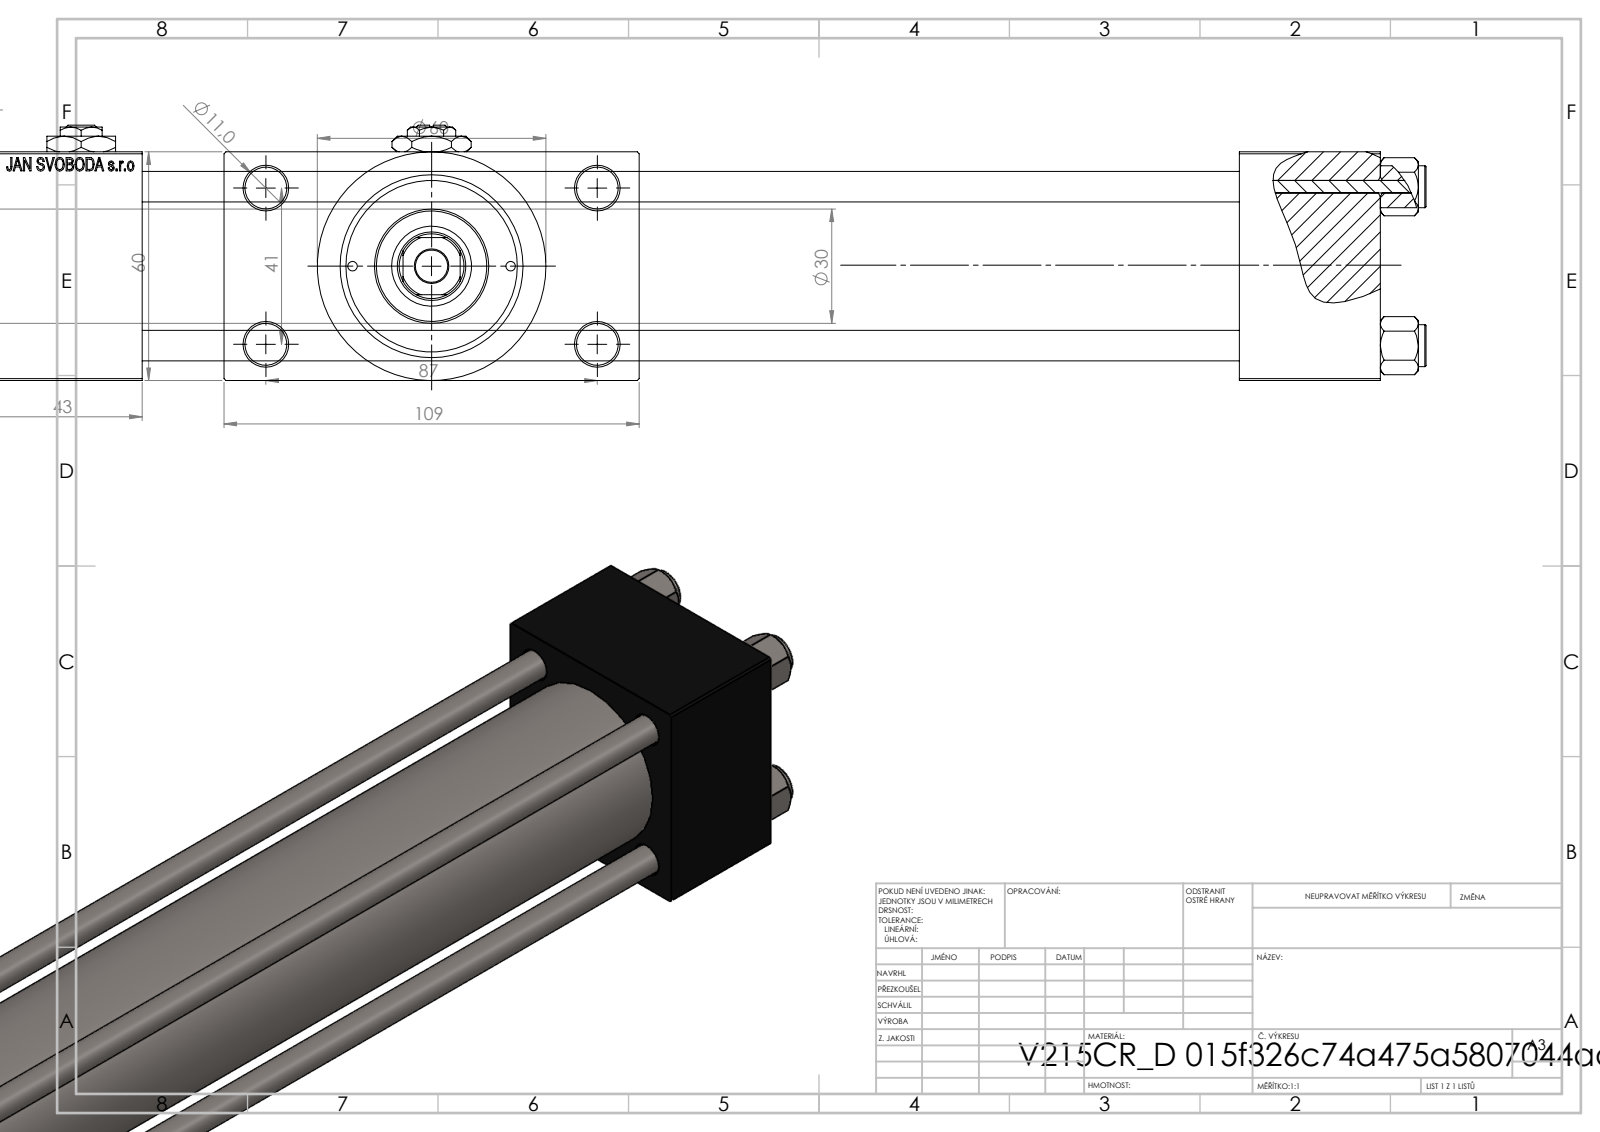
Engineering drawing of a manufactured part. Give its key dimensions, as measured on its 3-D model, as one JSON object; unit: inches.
{"part_name": "V215CR_D_Body; V215_VC_A; NUT_M5_D; V215CR_D_TYCINKA (+2 more)", "step_written_by": "SolidWorks 2019 (CONFIG_CONTROL_DESIGN)", "units": "inches", "bodies": {"solids": 12, "faces": 1160, "planar": 524, "cylindrical": 96, "other": 540}, "overall_size": [16.339, 4.291, 2.638], "volume_in3": 43.32, "surface_area_in2": 343.6, "round_holes": [[0.315, 4], [0.433, 4], [0.656, 3], [0.945, 3], [0.098, 2], [0.276, 2], [0.335, 1], [0.709, 1], [0.827, 1], [1.22, 1], [1.575, 1], [1.772, 1]], "round_bosses_or_shafts": [[0.433, 4], [2.362, 1], [1.811, 1], [1.181, 1]], "partial_cylinders_radius": [[0.335, 1]], "face_to_face_distances": [2.362, 11.339, 0.965, 3.327, 1.457, 12.795, 1.693, 14.488, 13.031, 0.394], "hole_center_spacings": [0.821, 0.892, 1.161, 1.206, 1.642, 1.832, 1.856, 1.893]}
